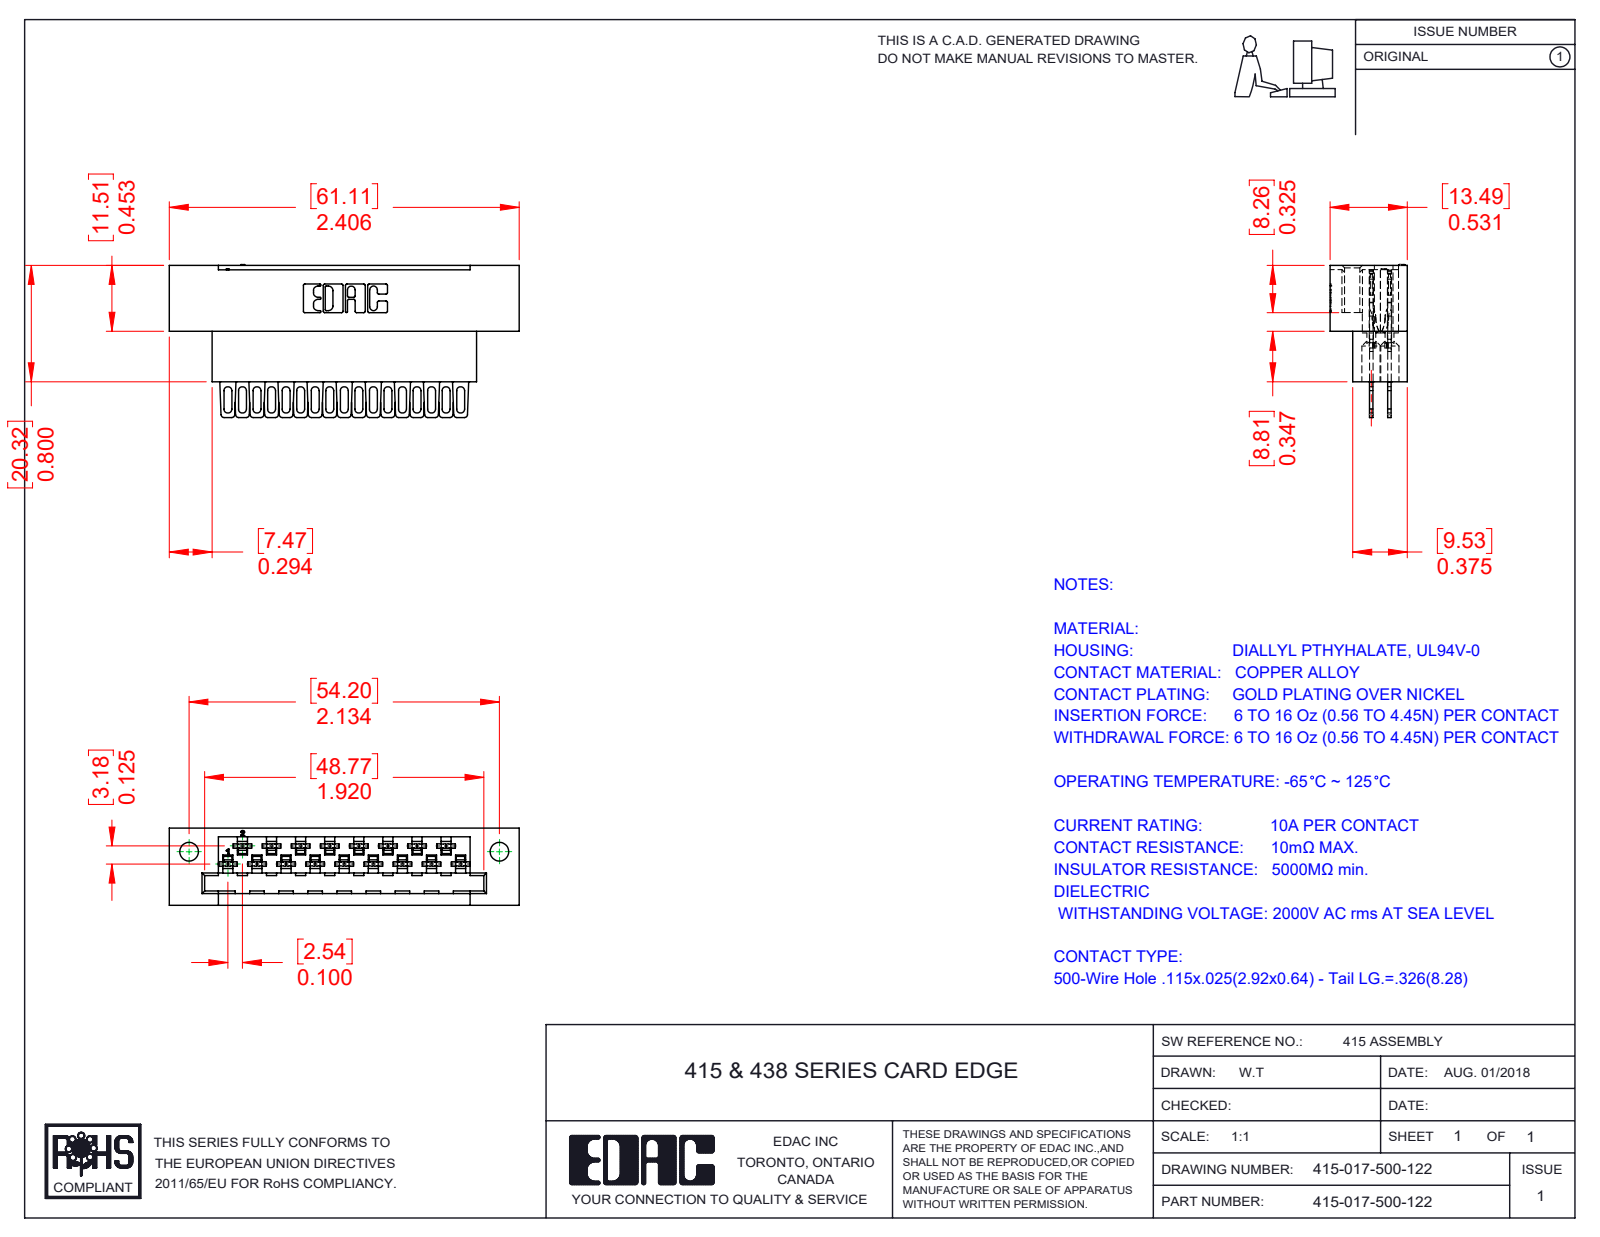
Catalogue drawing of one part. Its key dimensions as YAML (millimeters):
part_name: "516-290-001_500; 415-210-001_415-210-017-122; 415-017-500-122"
step_written_by: "SolidWorks 2016 (CONFIG_CONTROL_DESIGN)"
units: millimeters
bodies: {solids: 18, faces: 1878, planar: 1166, cylindrical: 537, other: 175}
overall_size: [61.11, 26.68, 13.49]
volume: 9908
surface_area: 11990
round_holes:
  - {diameter: 1.27, count: 17}
  - {diameter: 3.3, count: 17}
  - {diameter: 3.25, count: 2}
partial_cylinders:
  - {radius: 0.3, count: 68}
  - {radius: 0.56, count: 68}
  - {radius: 0.18, count: 34}
  - {radius: 0.2, count: 34}
  - {radius: 0.41, count: 34}
  - {radius: 0.51, count: 34}
  - {radius: 0.69, count: 34}
  - {radius: 2.03, count: 34}
face_to_face_distances: [3.18, 0.61, 13.49, 7.49, 1.27, 1.88, 20.32, 5.08, 6.61, 6.88]
hole_center_spacings: [5.08, 10.16, 15.24, 20.32, 2.54, 4.06, 7.62, 8.25]
